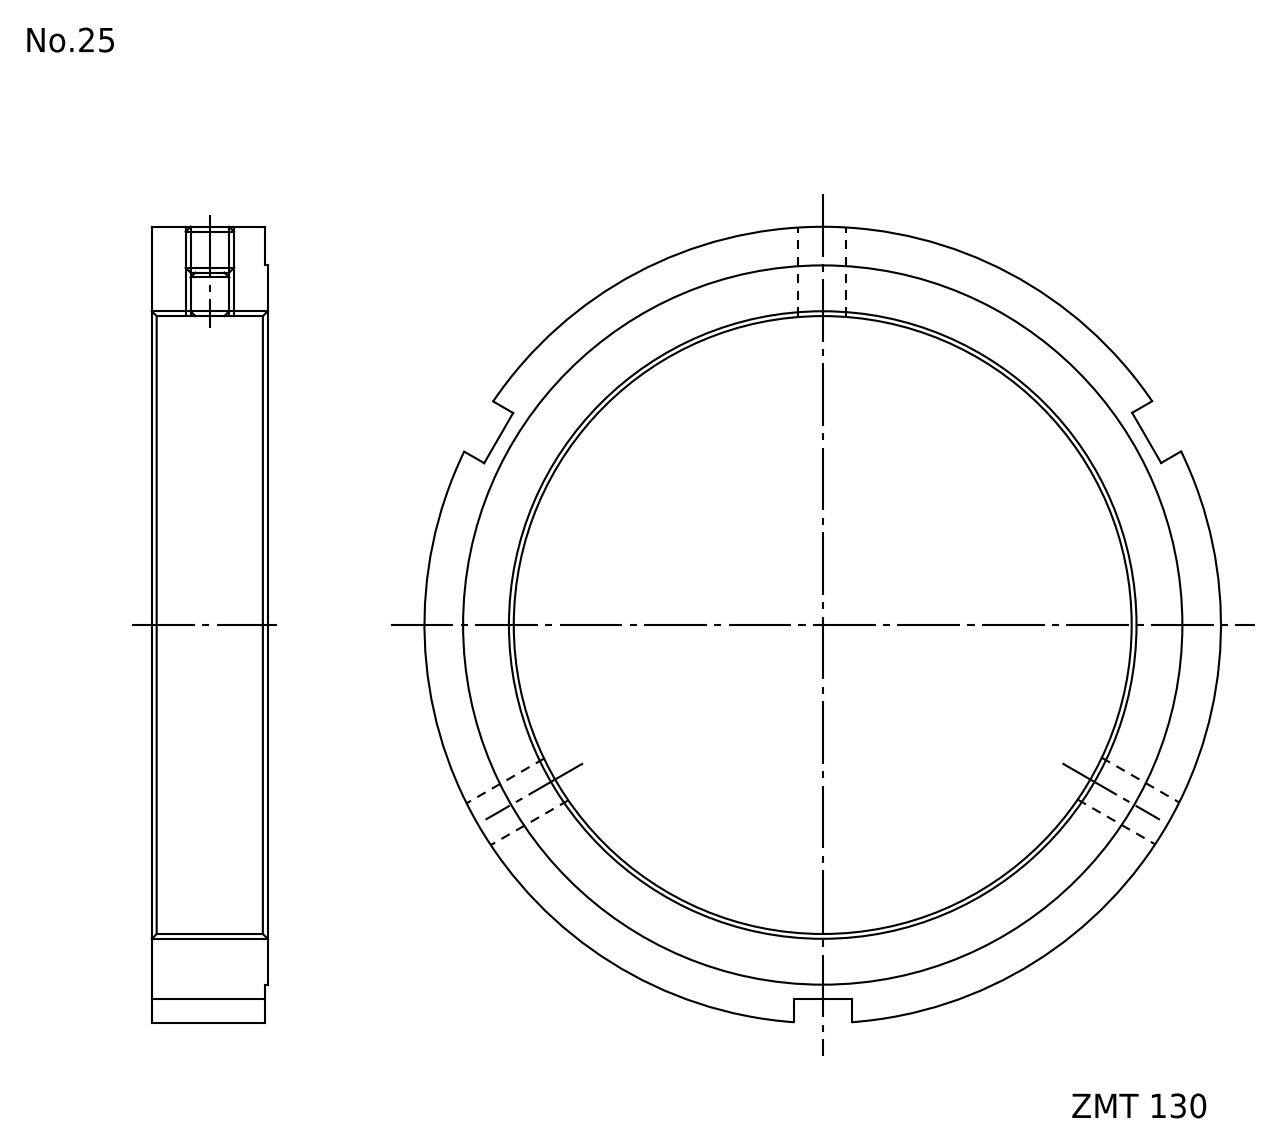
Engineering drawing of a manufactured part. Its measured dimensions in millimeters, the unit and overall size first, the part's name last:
Units: millimetres
Overall size (bounding box): 165 × 164.78 × 24
Round holes (diameter × count): ⌀8.38 ×3, ⌀130 ×1
Round bosses / shafts (diameter × count): ⌀165 ×1, ⌀149 ×1
Main face-to-face distances: 24, 0.5, 23.5, 12
Volume: 185 588 mm³ · Surface area: 39 806 mm²
Bodies: 1 solid, 20 faces (12 planar, 8 cylindrical, 0 other)
Part name (STEP PRODUCT): FKD ZMT130
STEP written by: Autodesk Inventor 2011 (AUTOMOTIVE_DESIGN)
